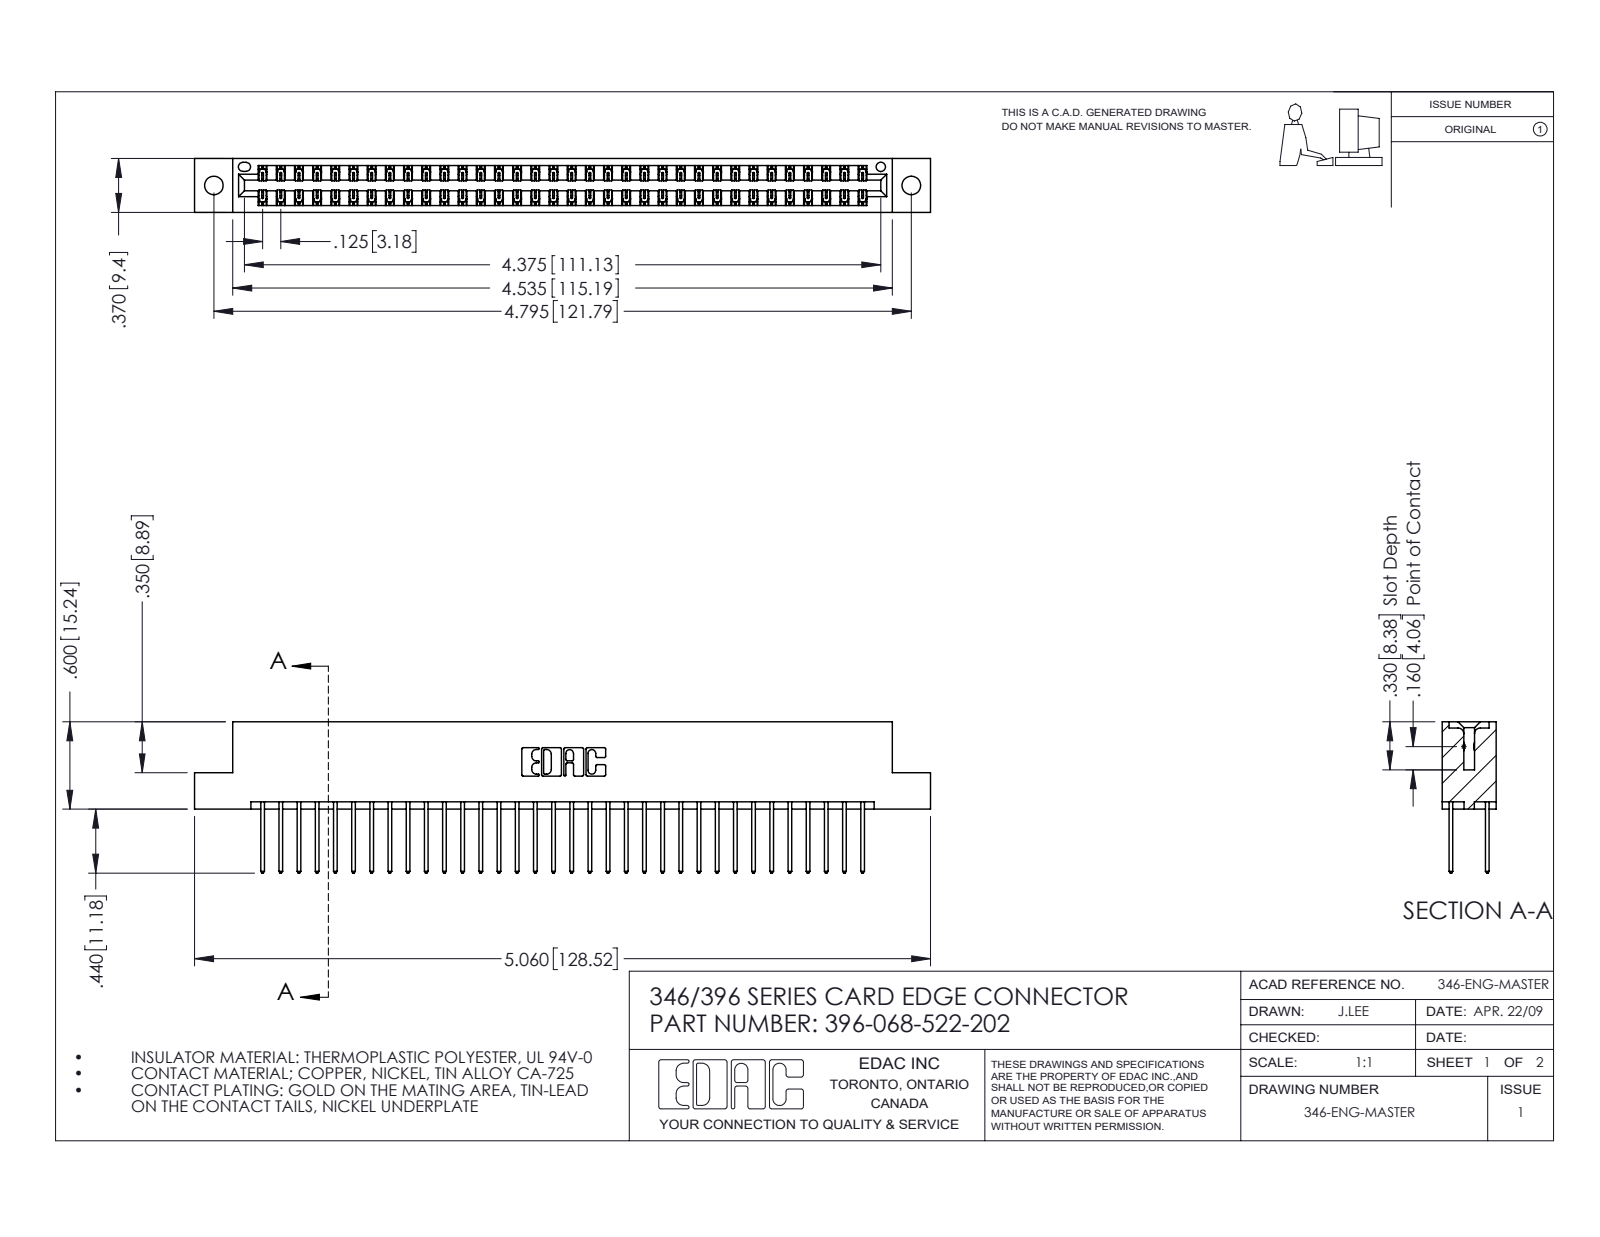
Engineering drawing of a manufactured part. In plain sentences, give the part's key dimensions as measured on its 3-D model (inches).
The part is named "345-292-001_345-293-122; 346 Part_Flush Mounting Lugs - 0.128 Dia; 396-068-522-202". Its 3-D file was written by "SolidWorks 2016 (CONFIG_CONTROL_DESIGN)". It is 69 solids with 3658 faces: 2456 planar, 1202 cylindrical and 0 other. Overall it measures 5.06 by 1.04 by 0.37 inches. Its volume is 0.769 cubic inches and its surface area 27.5 square inches. Round holes: 2 of diameter 0.128, 1 of diameter 0.064. Partial cylindrical surfaces (rounded edges, fillets, slot ends): 102 of radius 0.006, 68 of radius 0.01, 22 of radius 0.01, 6 of radius 0.007, 6 of radius 0.031, 3 of radius 0.026, 2 of radius 0.014, 2 of radius 0.022. The main face-to-face distances are 0.048, 0.322, 0.25, 0.37, 0.072, 0.298, 0.025, 0.275, 0.148, 0.222. The hole center spacings are 0.246, 4.587, 4.795.
